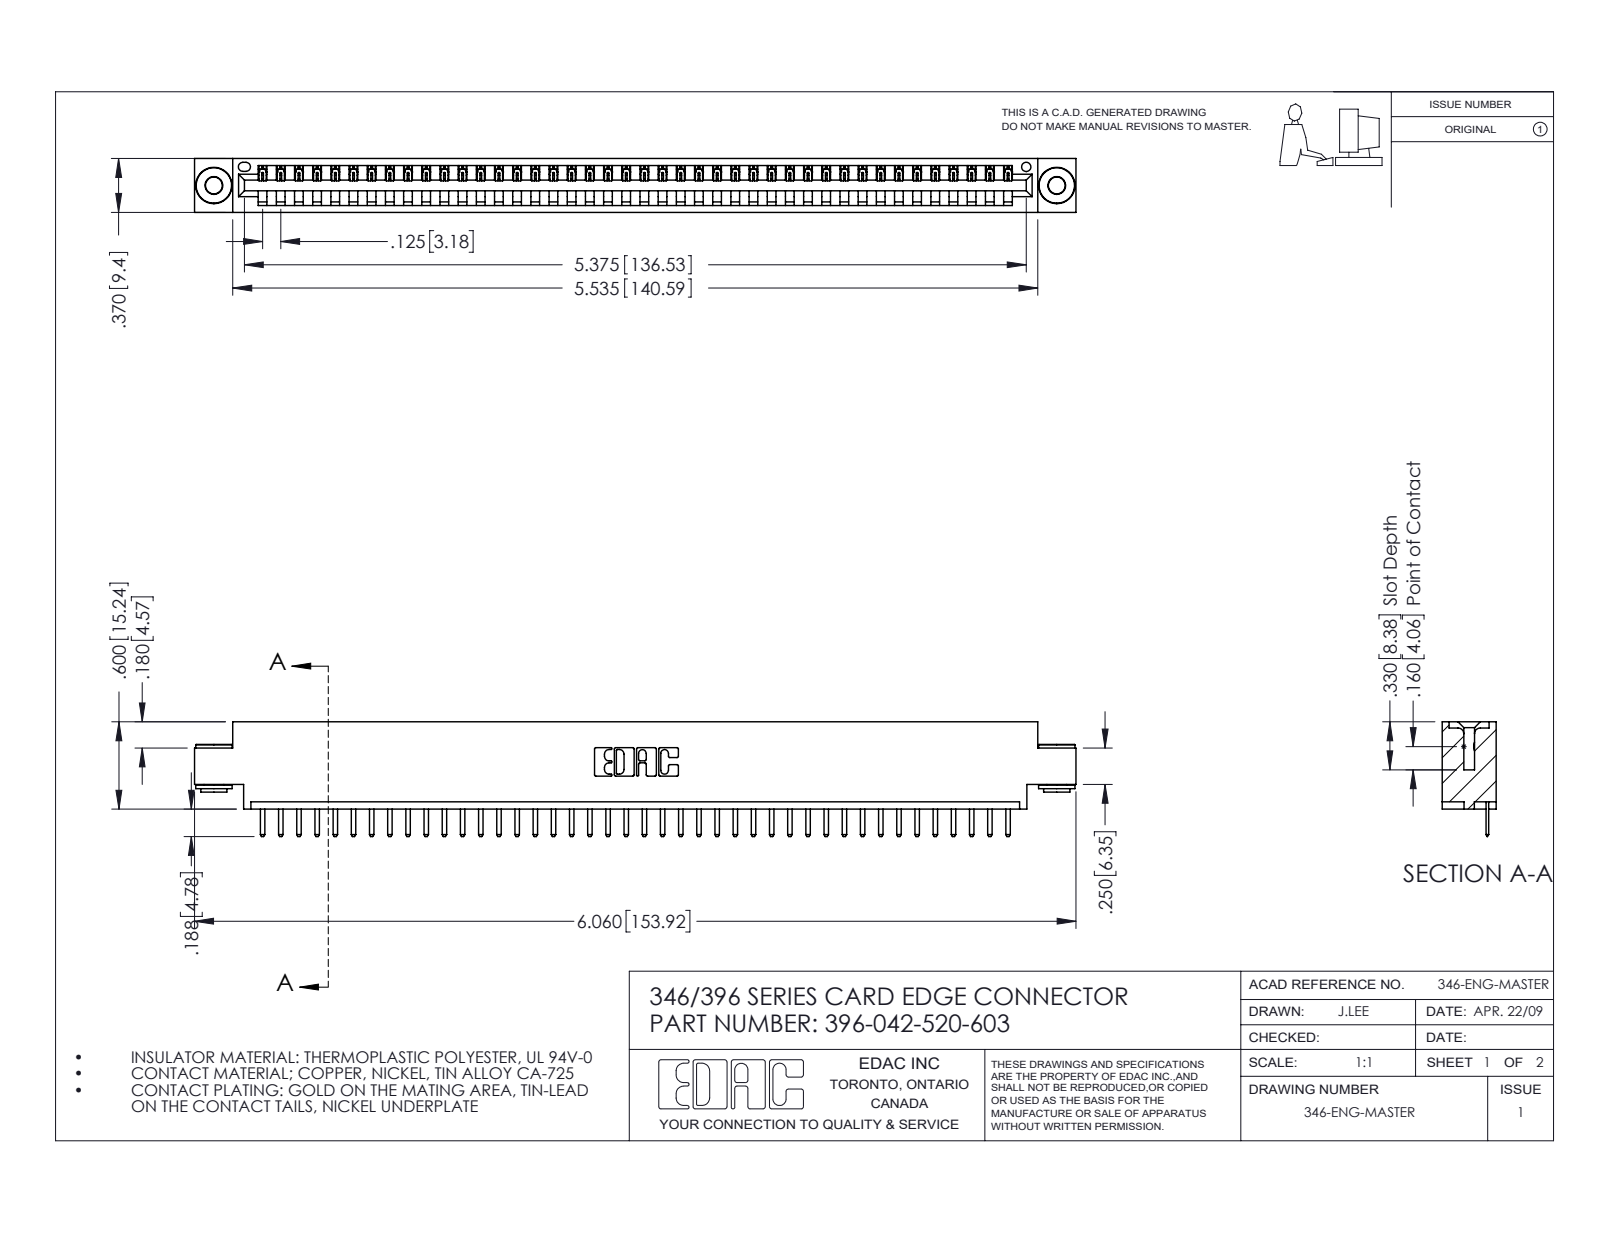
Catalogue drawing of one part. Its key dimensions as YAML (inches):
part_name: "396-042-520-603; 345-250-002_345-250-002-102; 346 Part_0.170 Offset - 0.156 Dia-TH; 345-292-001_345-293-120"
step_written_by: "SolidWorks 2016 (CONFIG_CONTROL_DESIGN)"
units: inches
bodies: {solids: 45, faces: 2768, planar: 1854, cylindrical: 906, other: 8}
overall_size: [6.06, 0.788, 0.37]
volume: 0.883
surface_area: 28.01
round_holes:
  - {diameter: 0.116, count: 2}
  - {diameter: 0.156, count: 2}
  - {diameter: 0.064, count: 1}
round_bosses_or_shafts:
  - {diameter: 0.25, count: 2}
  - {diameter: 0.18, count: 2}
  - {diameter: 0.136, count: 2}
partial_cylinders:
  - {radius: 0.01, count: 86}
  - {radius: 0.006, count: 84}
  - {radius: 0.01, count: 22}
  - {radius: 0.007, count: 6}
  - {radius: 0.031, count: 6}
  - {radius: 0.026, count: 3}
  - {radius: 0.031, count: 2}
  - {radius: 0.04, count: 2}
face_to_face_distances: [0.048, 0.322, 0.37, 0.25, 0.025, 0.148, 0.222, 0.1, 0.174, 0.072]
hole_center_spacings: [0.246, 5.586, 5.795]
